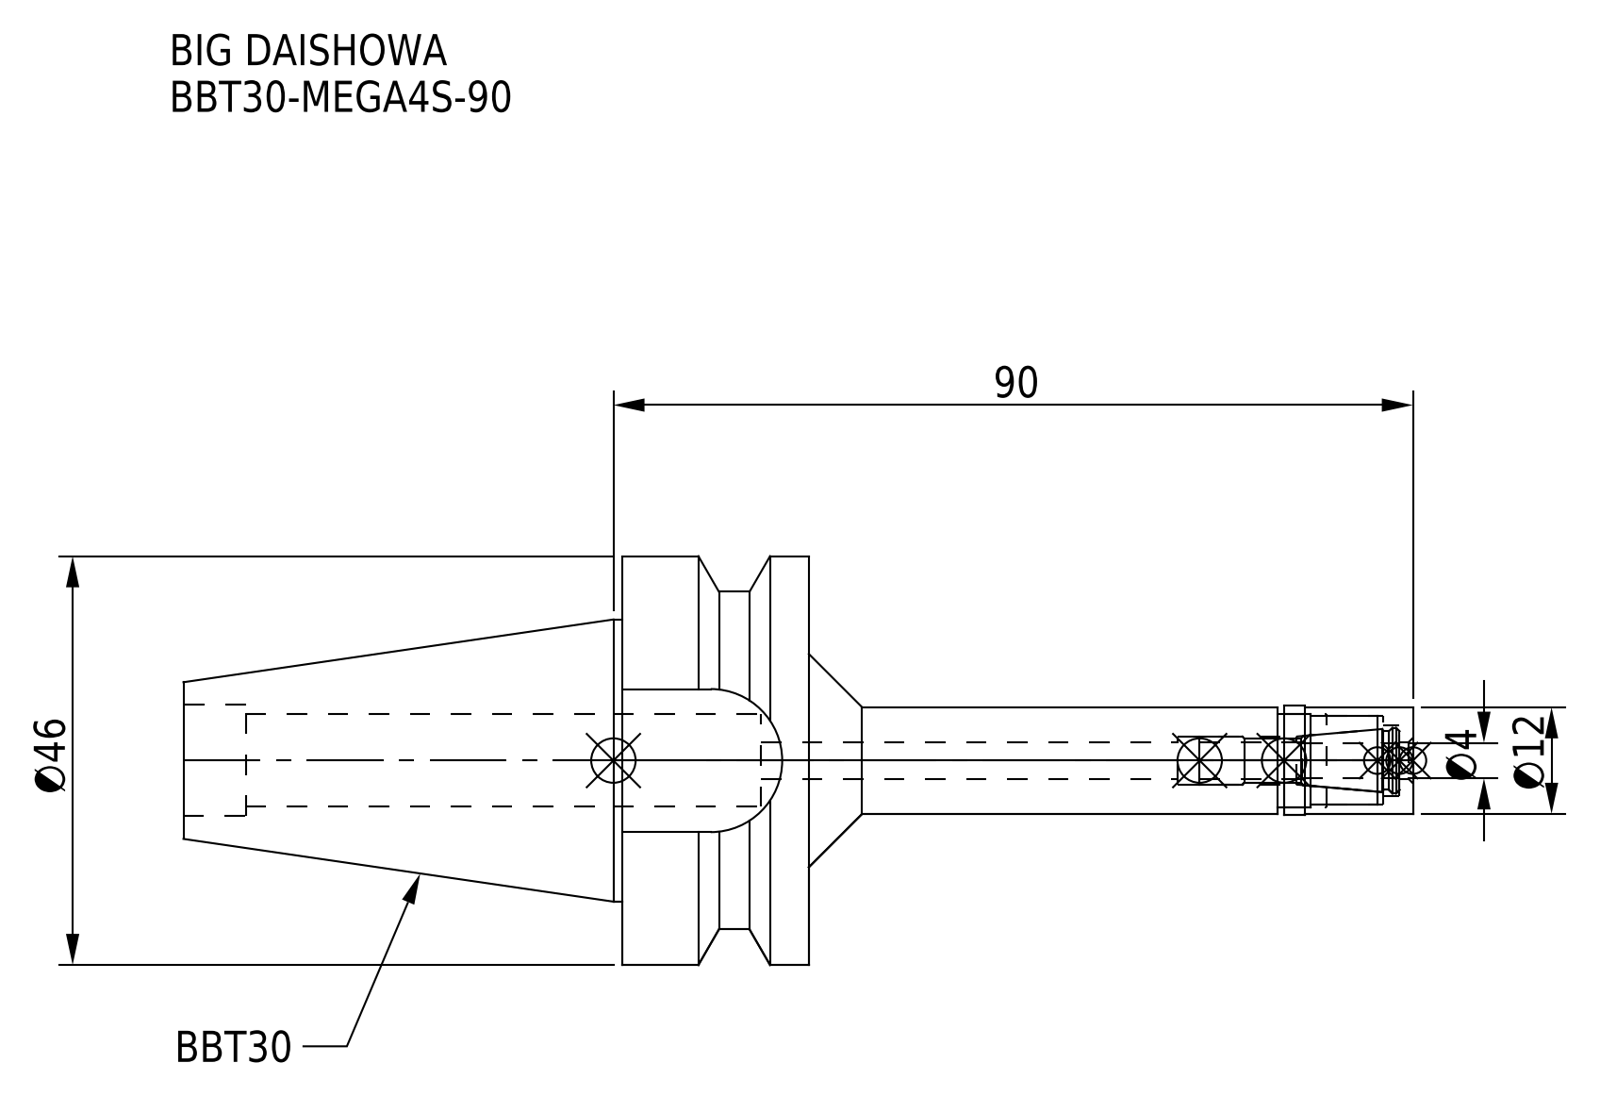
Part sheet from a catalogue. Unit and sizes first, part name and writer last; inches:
Units: inches
Overall size (bounding box): 5.449 × 1.811 × 1.811
Round holes (diameter × count): ⌀0.161 ×1, ⌀0.165 ×1, ⌀0.213 ×1, ⌀0.315 ×1, ⌀0.394 ×1, ⌀0.409 ×1, ⌀0.413 ×1, ⌀0.492 ×1
Round bosses / shafts (diameter × count): ⌀1.811 ×1, ⌀1.25 ×1, ⌀0.484 ×1, ⌀0.472 ×1, ⌀0.472 ×1, ⌀0.413 ×1, ⌀0.394 ×1
Partial cylindrical surfaces — rounded edges, fillets, slot ends (radius × count): R0.317 ×1, R0.748 ×1
Main face-to-face distances: 0.827, 1.283, 2.772, 1.945, 0.634, 2.677, 3.504, 5.449, 2.89, 0.213
Volume: 3.37 in³ · Surface area: 26.08 in²
Bodies: 2 solids, 71 faces (21 planar, 38 cylindrical, 12 other)
Part name (STEP PRODUCT): BBT30-MEGA4S-90; BBT30-MEGA4S-90-040.stp; BBT30MS04090-040_ASM.stp; BBT30-MEGA4S-90-040-FreeParts (+3 more)
STEP written by: SolidWorks 2019 (CONFIG_CONTROL_DESIGN)
